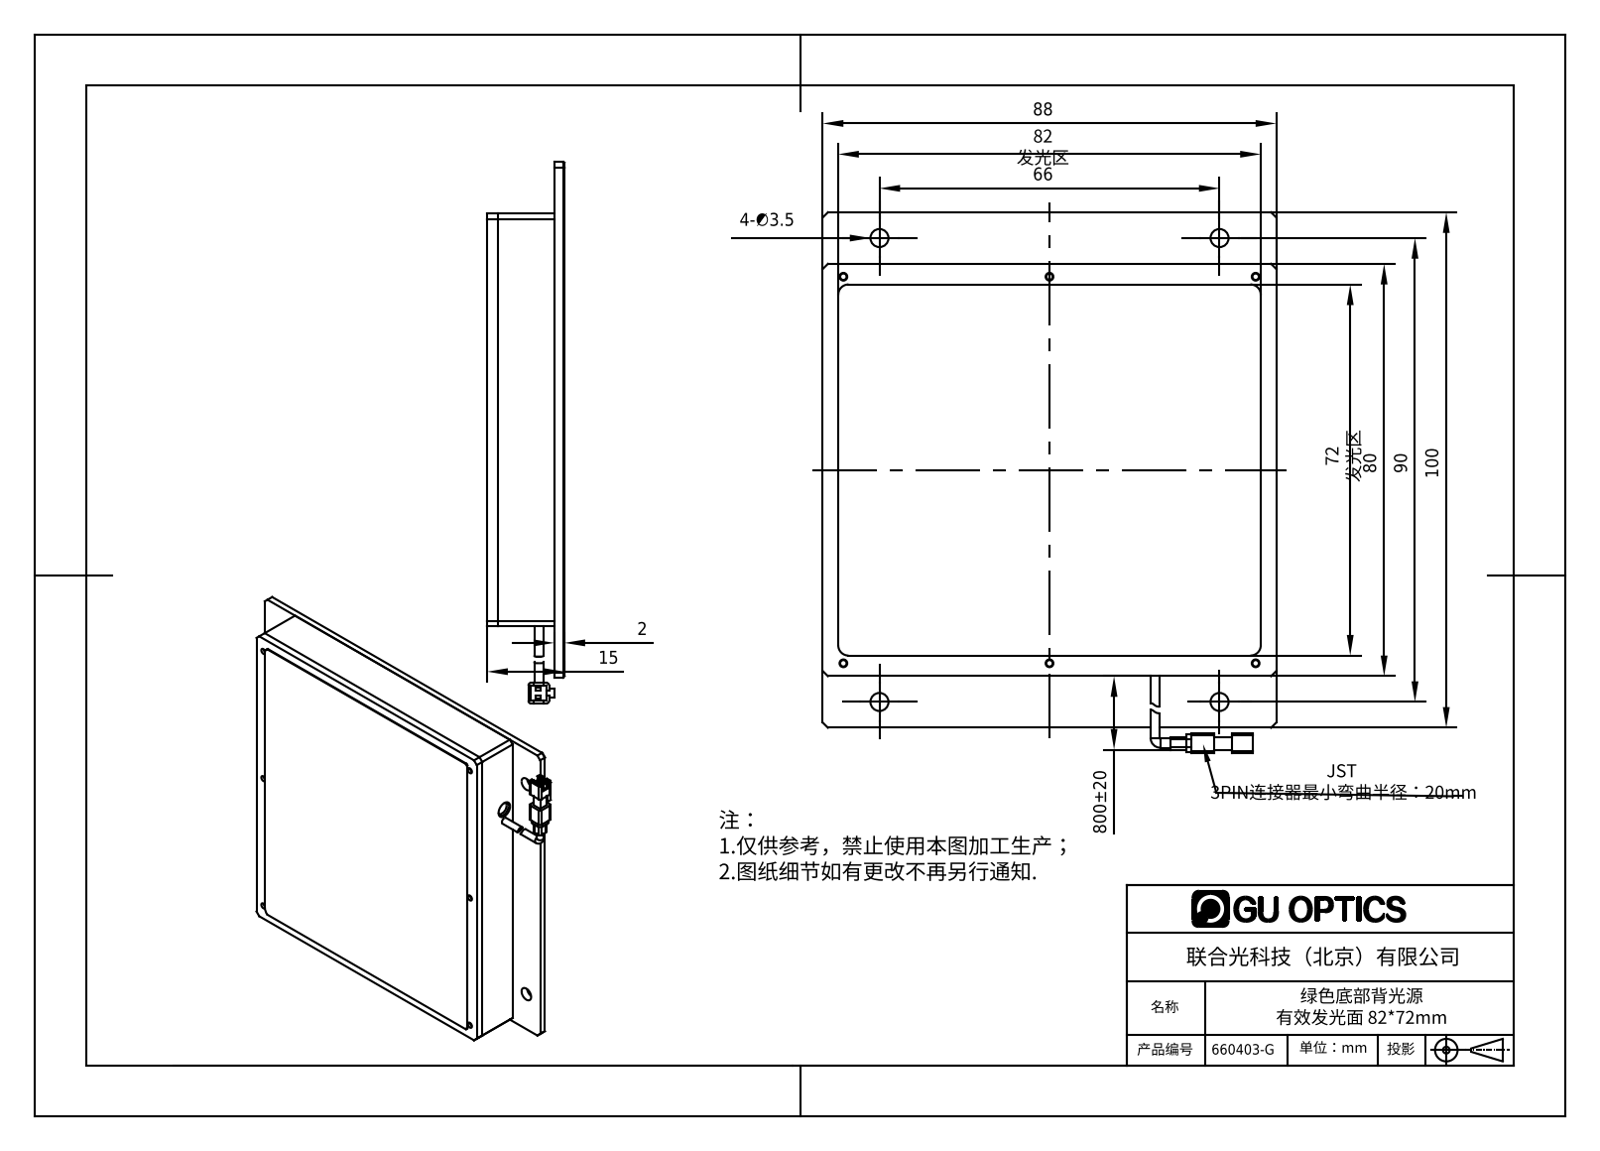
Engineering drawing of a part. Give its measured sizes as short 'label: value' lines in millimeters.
name: 660403-G
written by: SolidWorks 2016 (AUTOMOTIVE_DESIGN)
unit: mm
bodies: 5 solids, 421 faces (188 planar, 134 cylindrical, 99 other)
size: 105 × 88 × 15.2
volume: 44 726 mm³; area: 43 208 mm²
holes: 12× ⌀1.25, 12× ⌀1.6, 6× ⌀1.5, 6× ⌀2.4, 6× ⌀2.8, 4× ⌀3.5, 1× ⌀3.6
bosses: 2× ⌀1.75
rounds: 8× R0.5, 8× R1, 4× R2, 2× R1.5, 1× R0.65, 1× R0.65, 1× R1.71, 1× R1.98
face distances: 2, 13, 11, 2.2, 15.2, 13.2, 3, 4, 76, 85
hole spacings: 40, 80, 85.44, 0.5, 75.5, 9.9, 10.26, 33.73
